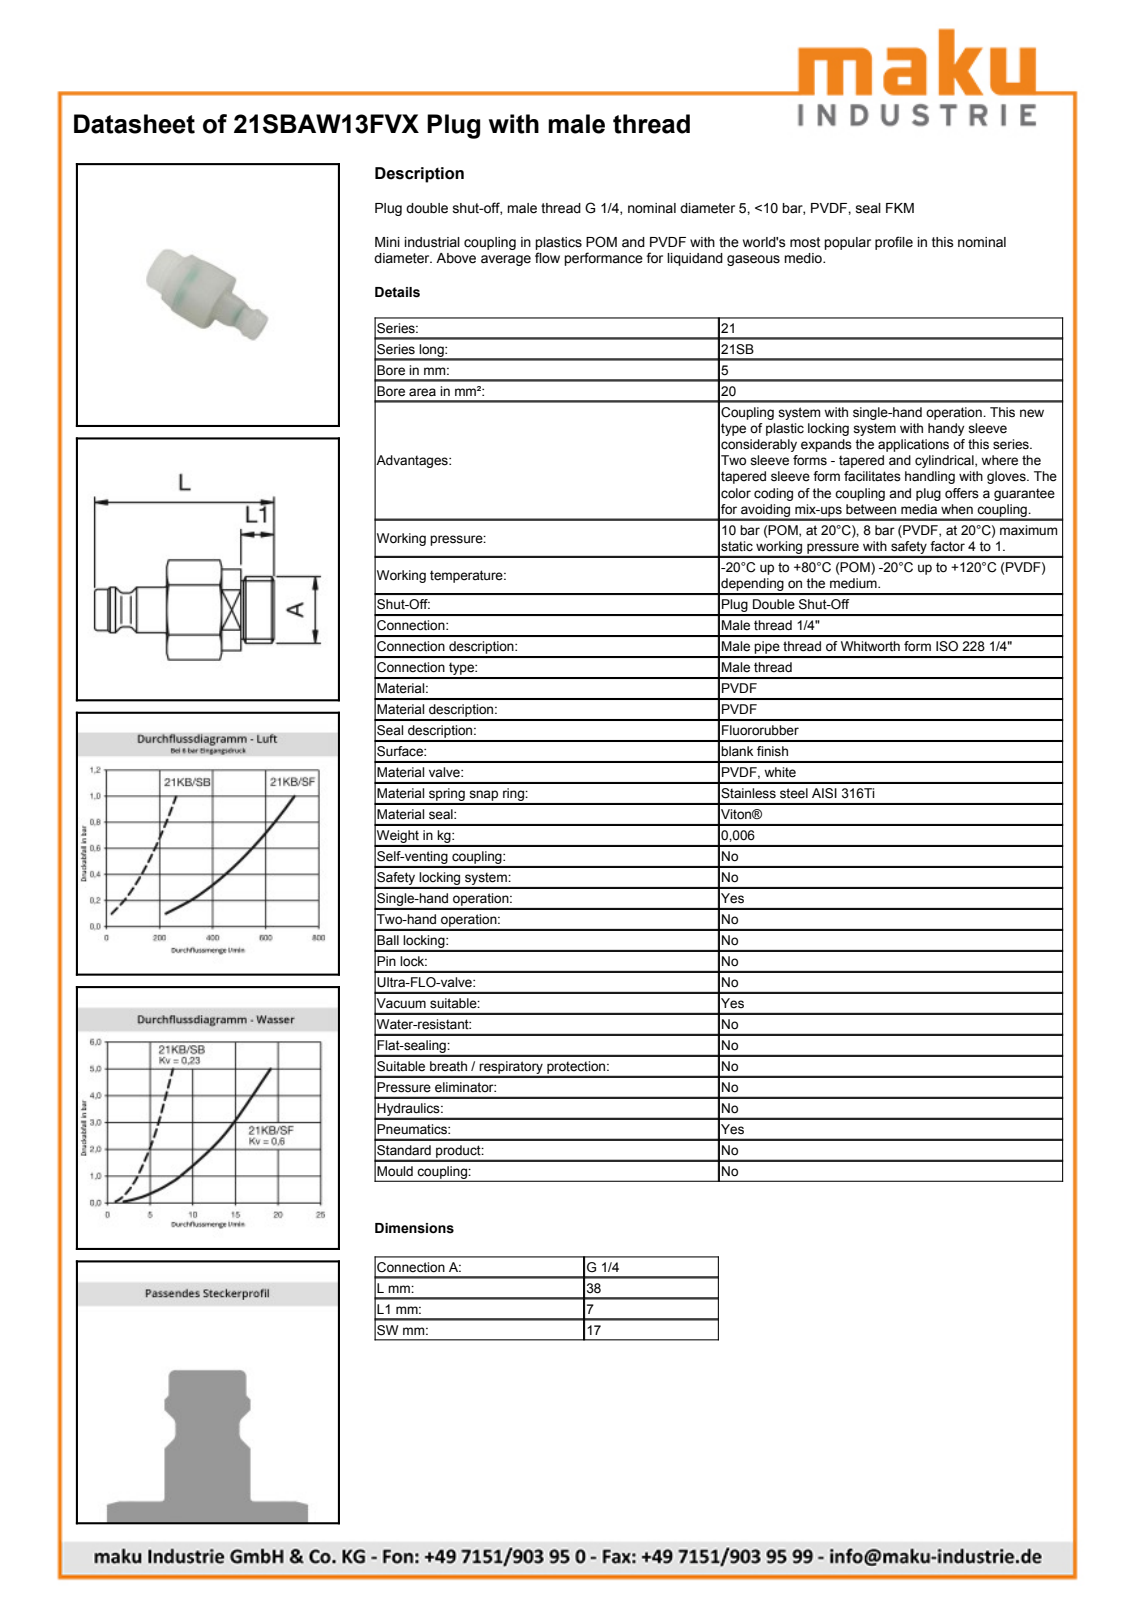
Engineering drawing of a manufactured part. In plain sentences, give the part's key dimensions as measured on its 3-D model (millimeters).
The part is named "D106212". Its 3-D file was written by "Autodesk Inventor 2011 (AUTOMOTIVE_DESIGN)". It is 1 solid with 51 faces: 16 planar, 14 cylindrical and 21 other. Overall it measures 35.8 by 19.63 by 17 millimeters. Its volume is 4 922 cubic millimeters and its surface area 2 401 square millimeters. Round holes: 1 of diameter 13.3. Round bosses or shafts: 1 of diameter 13.16, 1 of diameter 11.45, 1 of diameter 10.5, 1 of diameter 9.45, 1 of diameter 9, 1 of diameter 8.85, 1 of diameter 8.15, 1 of diameter 6.65. Partial cylindrical surfaces (rounded edges, fillets, slot ends): 1 of radius 8. The main face-to-face distances are 17, 10.8, 8, 21.65, 10.85, 13.65, 2.8, 14.15, 25, 27.8.
